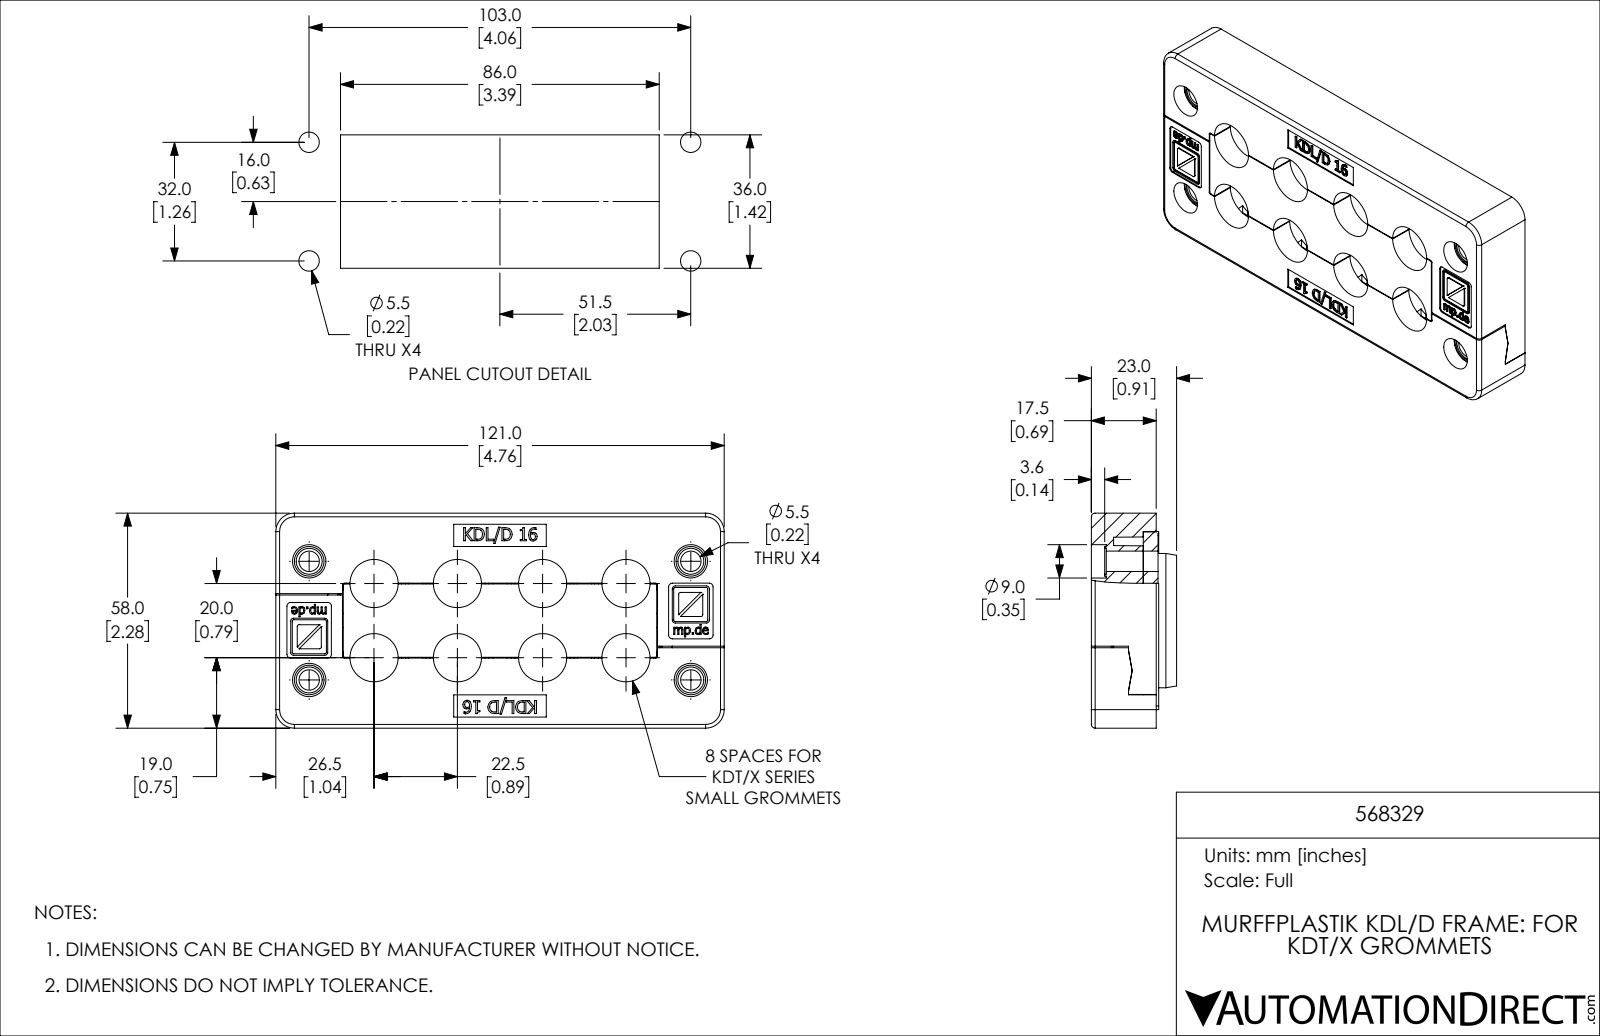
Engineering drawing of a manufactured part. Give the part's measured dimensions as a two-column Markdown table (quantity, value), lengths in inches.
| quantity | value |
| --- | --- |
| part name | 568329 |
| STEP written by | SolidWorks 2019 (CONFIG_CONTROL_DESIGN) |
| units | inches |
| bodies | 4 solids, 1436 faces (833 planar, 324 cylindrical, 279 other) |
| overall size | 4.764 × 2.283 × 0.906 |
| volume | 5.726 in³ |
| surface area | 82.76 in² |
| round holes (diameter × count) | 0.512 × 8, 0.589 × 8, 0.197 × 6, 0.217 × 4, 0.276 × 4, 0.354 × 4, 0.16 × 2, 0.236 × 2 |
| round bosses / shafts (diameter × count) | 0.315 × 4 |
| partial cylindrical surfaces (radius × count) | 0.02 × 64, 0.039 × 30, 0.016 × 12, 0.031 × 8, 0.333 × 8, 0.006 × 4, 0.012 × 4, 0.08 × 4 |
| main face-to-face distances | 0.197, 0.138, 0.157, 2.087, 0.551, 0.236, 0.02, 0.453, 0.709, 0.354 |
| hole center spacings | 0.394, 0.728, 0.787, 0.886, 0.969, 0.987, 1.185, 1.234 |
